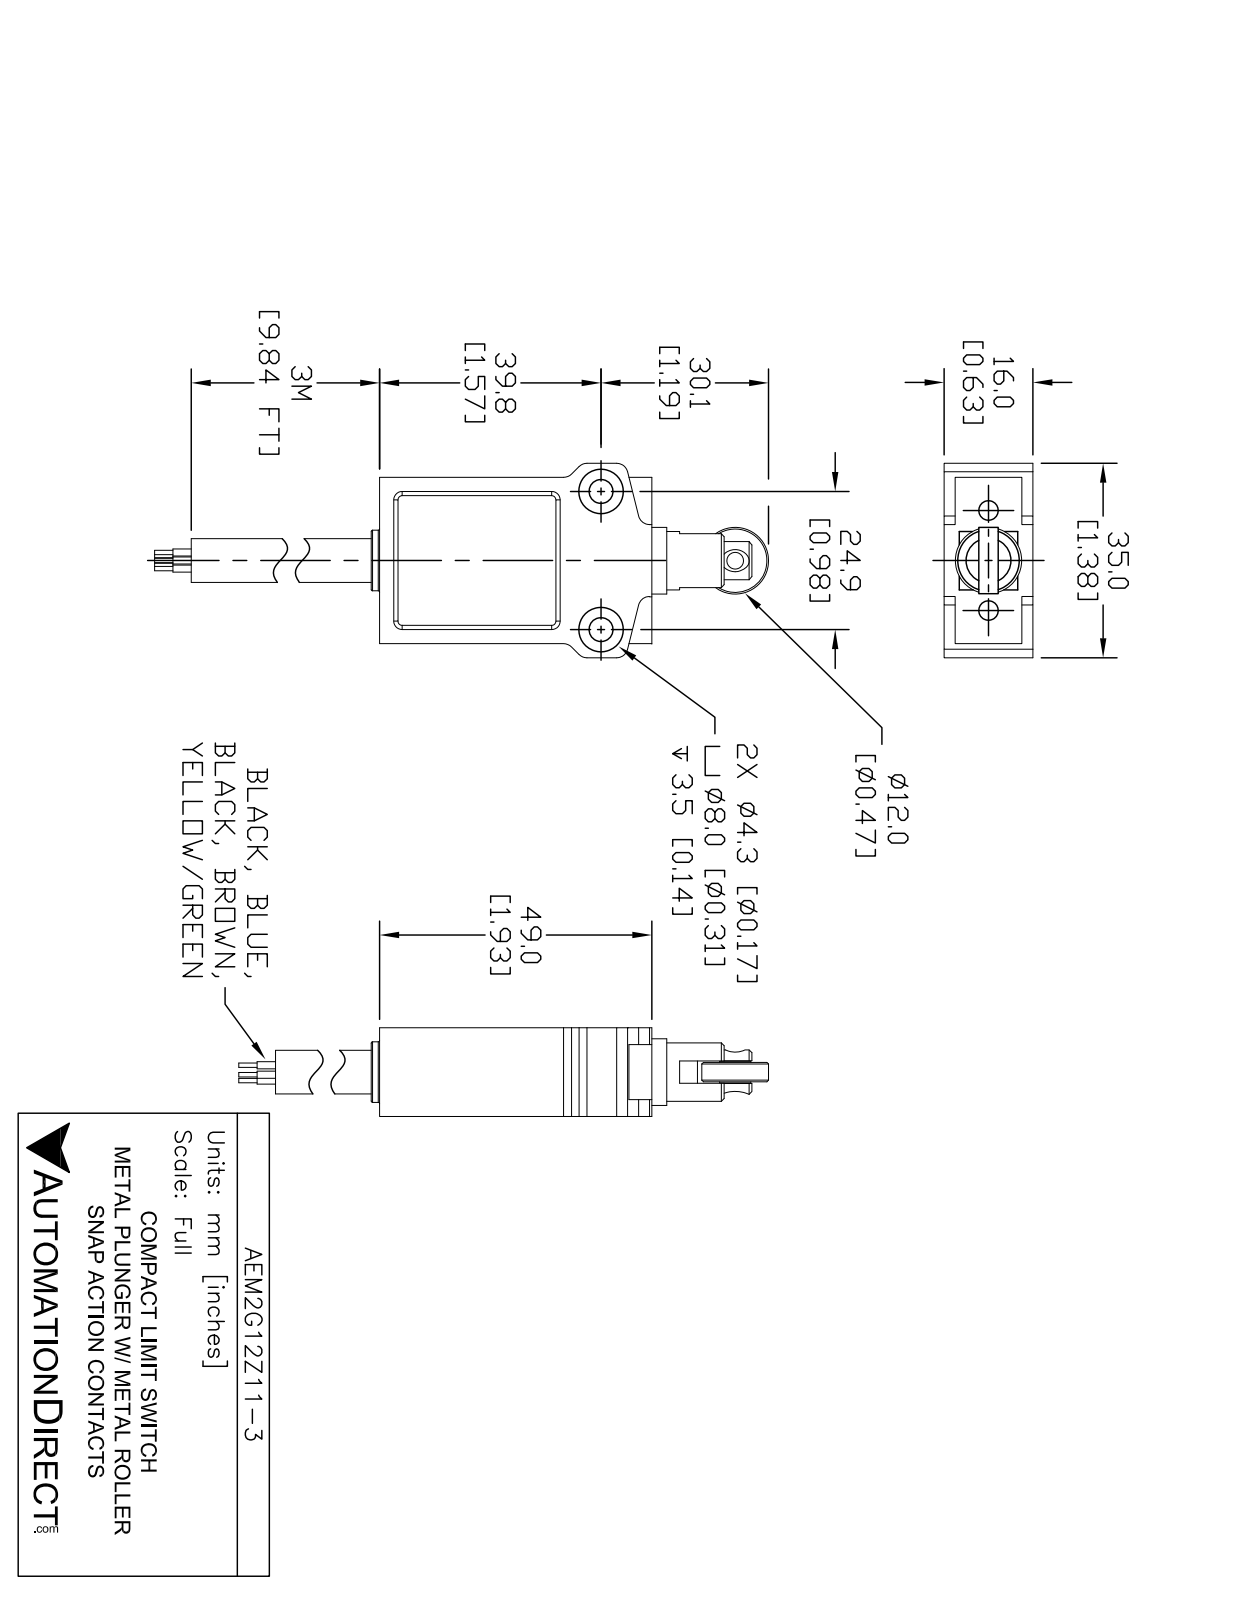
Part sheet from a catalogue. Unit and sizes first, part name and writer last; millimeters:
Units: millimetres
Overall size (bounding box): 85.7 × 35.1 × 16
Round holes (diameter × count): ⌀3.5 ×2, ⌀4.5 ×2, ⌀8.7 ×2
Round bosses / shafts (diameter × count): ⌀1.3 ×5, ⌀0.8 ×5, ⌀11.9 ×2, ⌀10.9 ×1, ⌀10.4 ×1, ⌀7.9 ×1
Partial cylindrical surfaces — rounded edges, fillets, slot ends (radius × count): R0.8 ×8, R2 ×8, R3.4 ×1
Main face-to-face distances: 0.8, 15.2, 14.5, 16, 30, 49, 6, 10, 5.2, 9.3
Hole centre spacings: 17.8, 24.9
Volume: 23 380 mm³ · Surface area: 7 723 mm²
Bodies: 2 solids, 116 faces (53 planar, 43 cylindrical, 20 other)
Part name (STEP PRODUCT): AEM2G12Z11-3_Default
STEP written by: SolidWorks 2021 (CONFIG_CONTROL_DESIGN)
